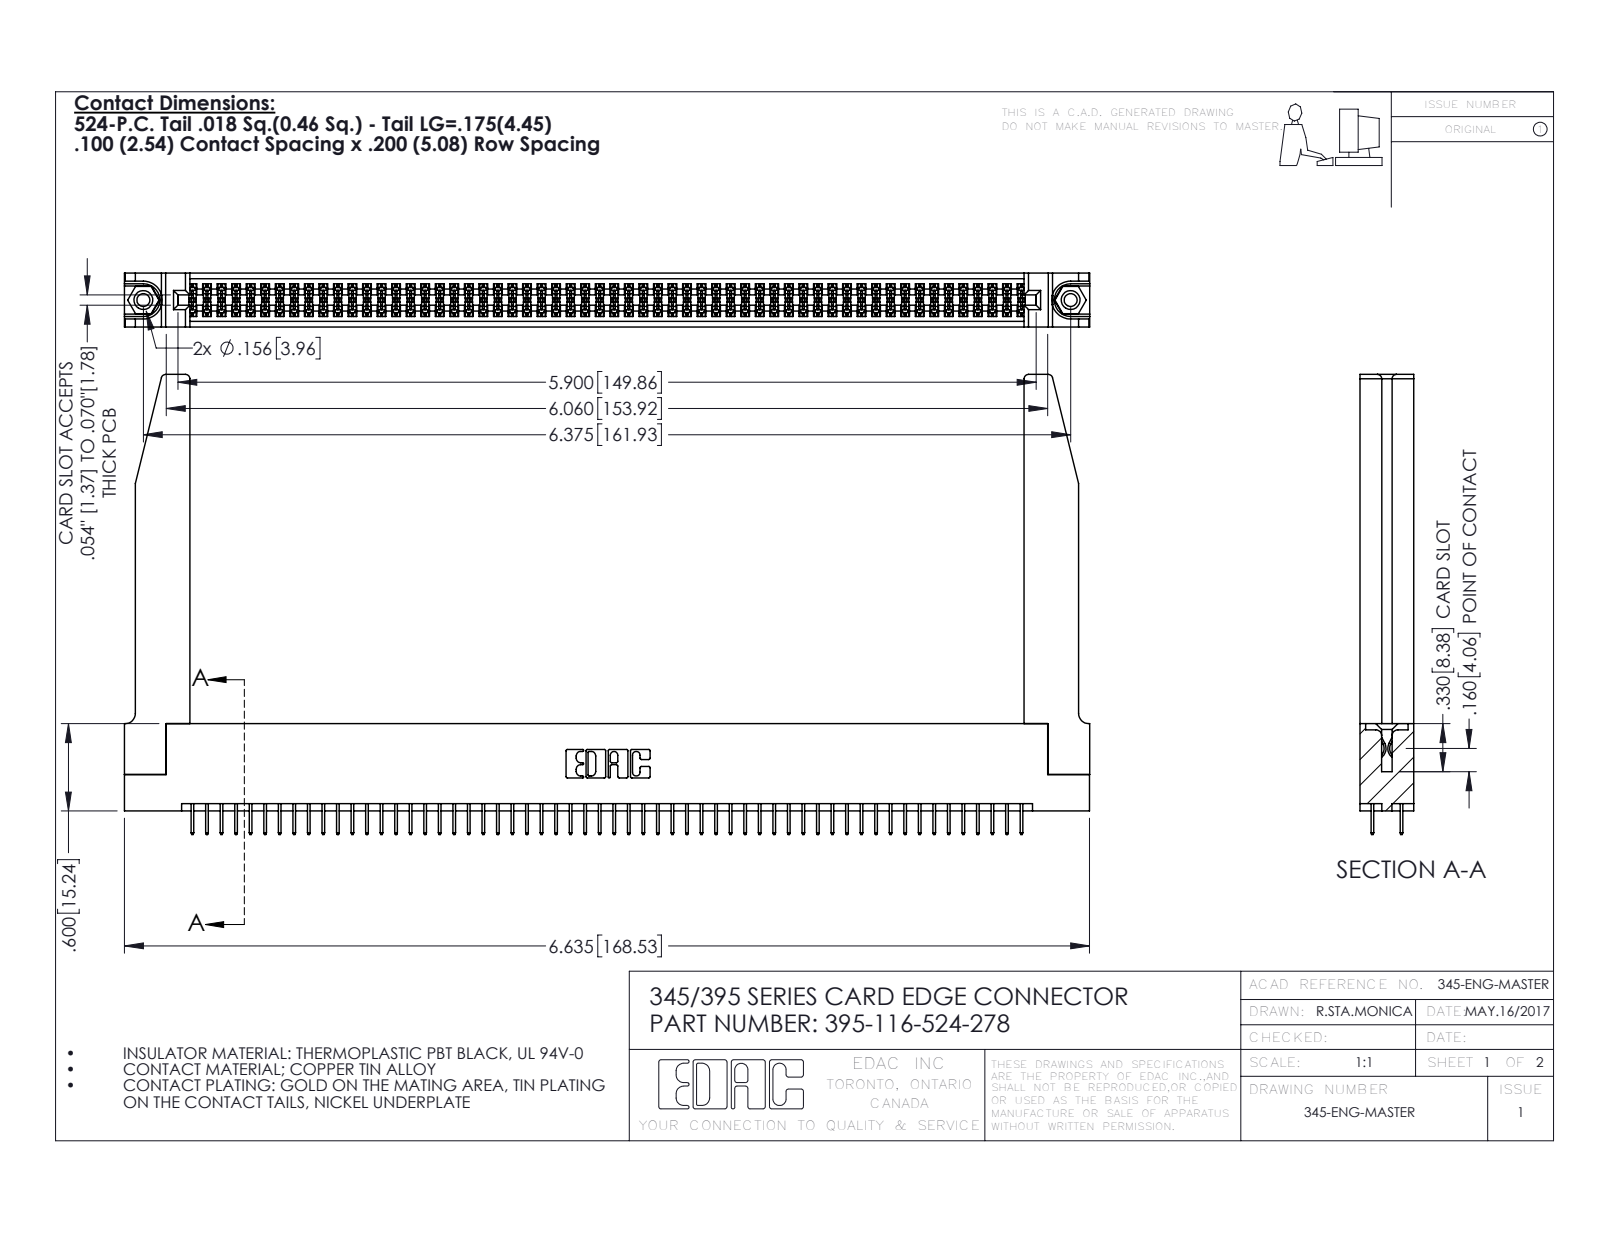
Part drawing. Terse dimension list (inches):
name: 345-292-001_345-293-124; 345 Part_Flush Mounting Lugs - 0.156 Dia-TH; 345-220-078_345-220-078; 345-250-001_345-250-001-102 (+1 more)
written by: SolidWorks 2016 (CONFIG_CONTROL_DESIGN)
unit: in
bodies: 121 solids, 6624 faces (4746 planar, 1826 cylindrical, 52 other)
size: 6.636 × 3.162 × 0.37
volume: 1.472 in³; area: 47.81 in²
holes: 2× ⌀0.089, 2× ⌀0.125, 2× ⌀0.156, 1× ⌀0.064
bosses: 2× ⌀0.155
rounds: 174× R0.006, 22× R0.01, 8× R0.03, 6× R0.007, 6× R0.031, 3× R0.026, 2× R0.014, 2× R0.019
face distances: 0.072, 0.37, 0.298, 0.2, 0.098, 0.272, 0.025, 0.225, 0.072, 0.175
hole spacings: 0.27, 6.139, 6.375
